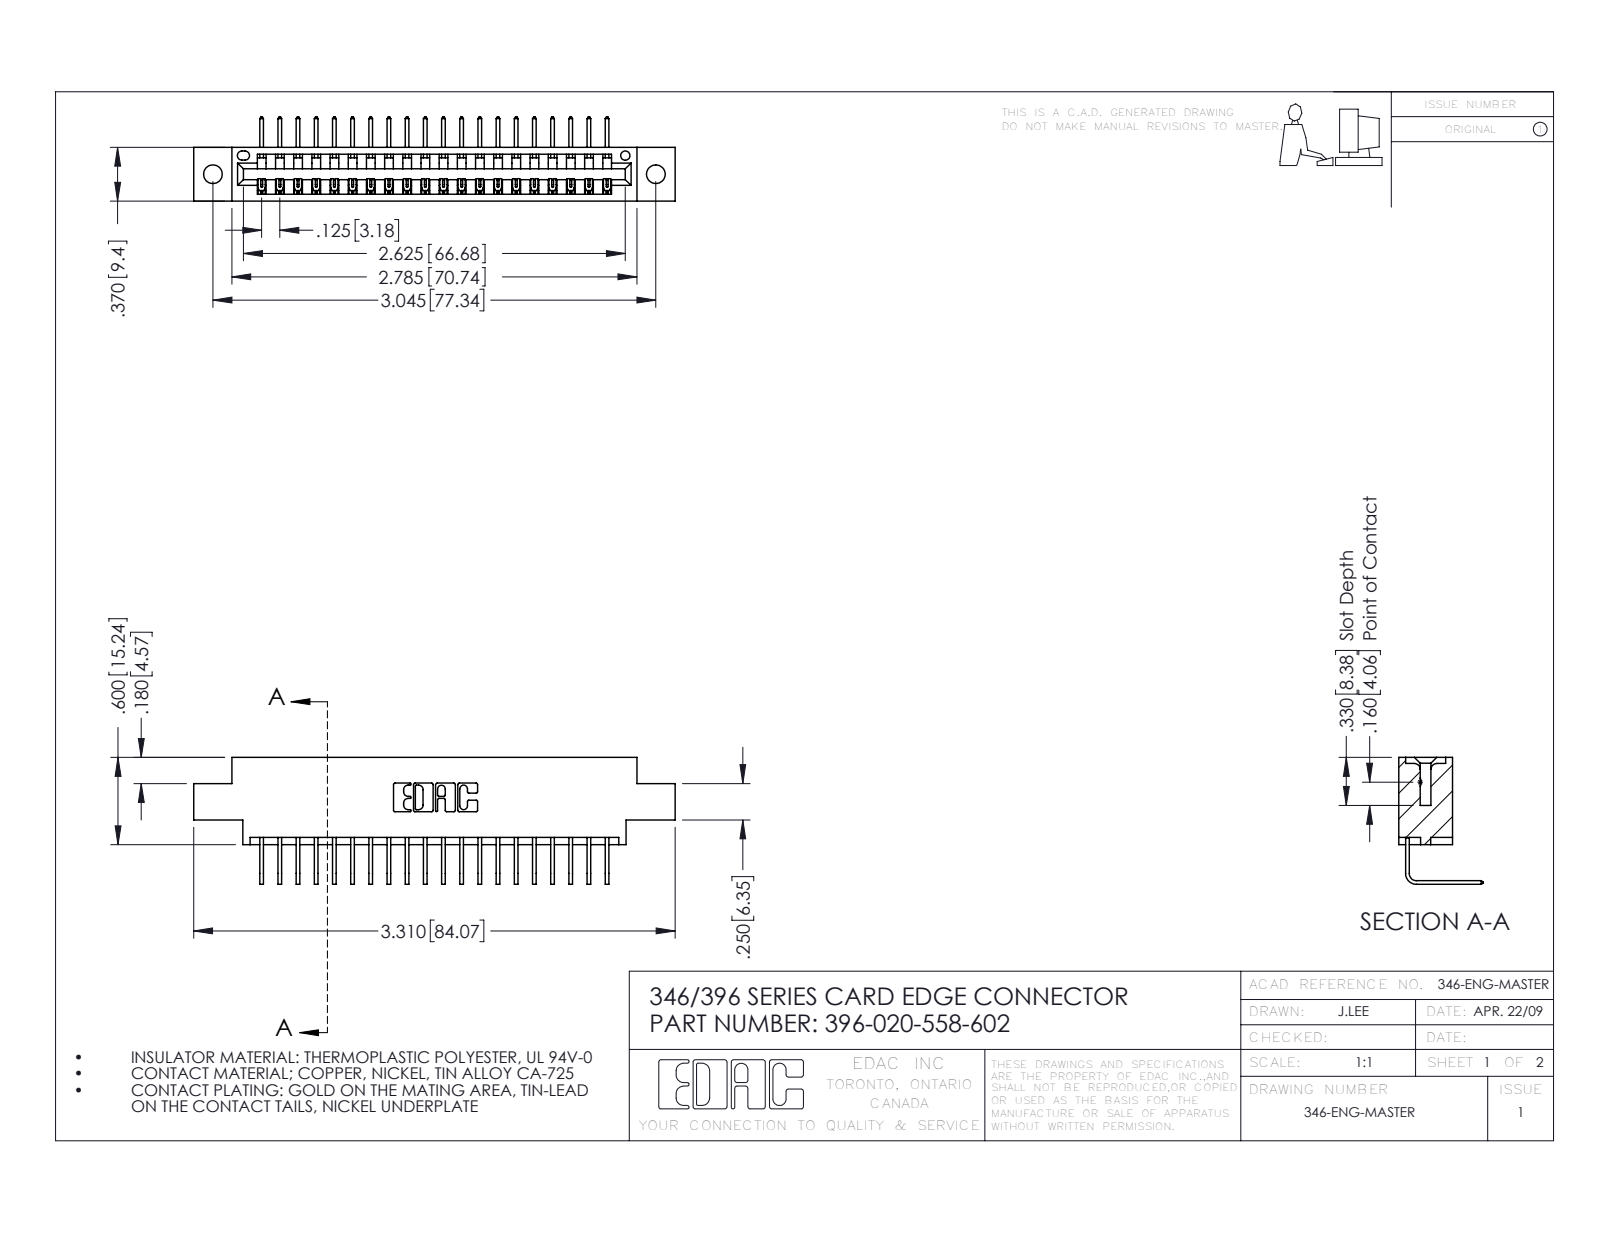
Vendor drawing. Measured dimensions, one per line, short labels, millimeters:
name: 346 Part_0.170 Offset - 0.128 Dia; 345-292-001_558 Tail - 2; 396-020-558-602
written by: SolidWorks 2016 (CONFIG_CONTROL_DESIGN)
unit: mm
bodies: 21 solids, 1326 faces (920 planar, 406 cylindrical, 0 other)
size: 84.1 × 22.2 × 14.7
volume: 7 770 mm³; area: 9 761 mm²
holes: 2× ⌀3.3, 1× ⌀1.6
rounds: 40× R0.2, 22× R0.3, 6× R0.2, 6× R0.8, 3× R0.7, 2× R0.8, 2× R1, 1× R0.4
face distances: 8.2, 1.2, 9.4, 6.4, 7.6, 0.6, 1.8, 3.8, 5.6, 2.5
hole spacings: 6.2, 72.1, 77.3
